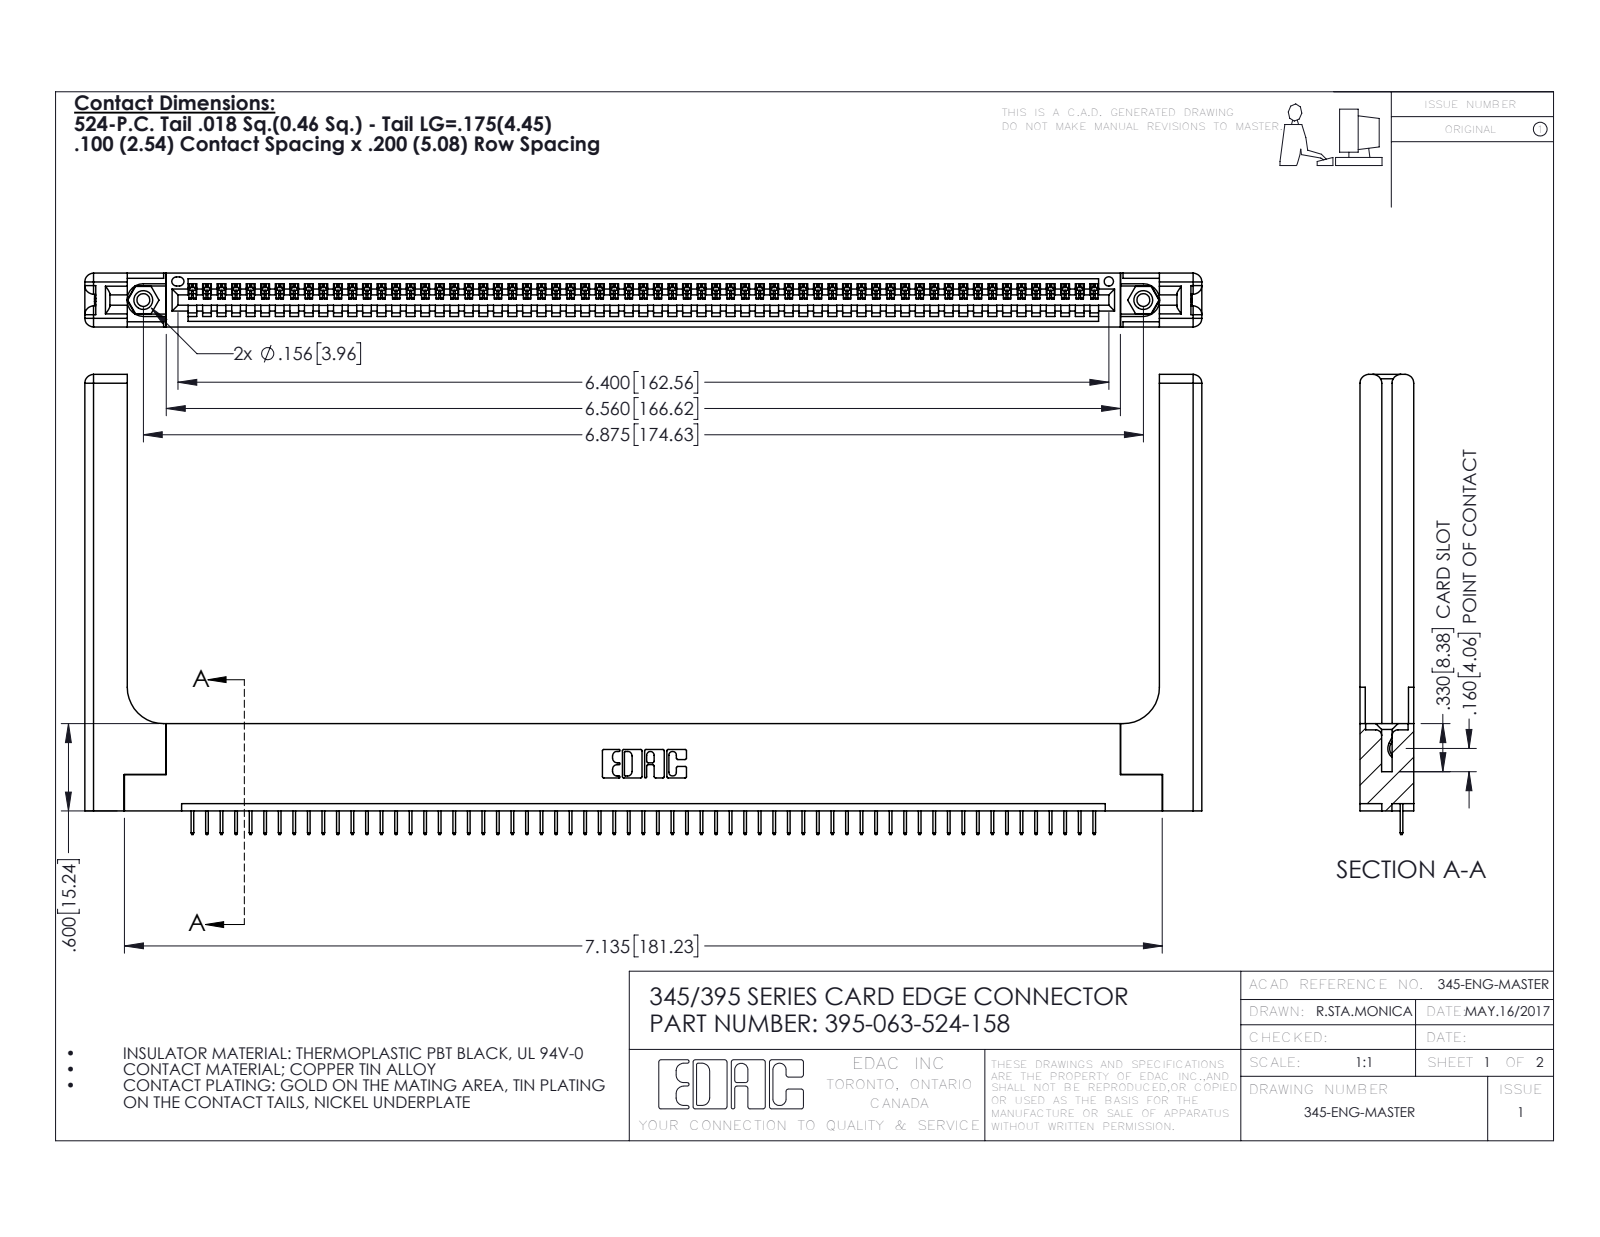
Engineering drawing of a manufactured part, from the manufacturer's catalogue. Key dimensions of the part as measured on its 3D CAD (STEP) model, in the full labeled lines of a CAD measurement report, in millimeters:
Part name (STEP PRODUCT): 345-292-001_345-293-124; 345-250-001_345-250-001-102; 345 Part_Flush Mounting Lugs - 0.156 Dia-TH; 395-063-524-158 (+1 more)
STEP written by: SolidWorks 2016 (CONFIG_CONTROL_DESIGN)
Units: millimetres
Bodies: 68 solids, 4288 faces (3126 planar, 1102 cylindrical, 60 other)
Overall size (bounding box): 195 × 80.3 × 9.4
Volume: 26 960 mm³ · Surface area: 29 310 mm²
Round holes (diameter × count): ⌀2.3 ×2, ⌀3.2 ×2, ⌀4 ×2, ⌀1.6 ×1
Round bosses / shafts (diameter × count): ⌀3.9 ×2
Partial cylindrical surfaces — rounded edges, fillets, slot ends (radius × count): R0.2 ×126, R0.3 ×22, R1.5 ×16, R0.2 ×6, R0.8 ×6, R0.7 ×3, R0.8 ×2, R0.8 ×2
Main face-to-face distances: 1.8, 9.4, 7.6, 5.1, 2.5, 6.9, 0.6, 5.7, 3.8, 3.8
Hole centre spacings: 6.9, 168.6, 174.6
